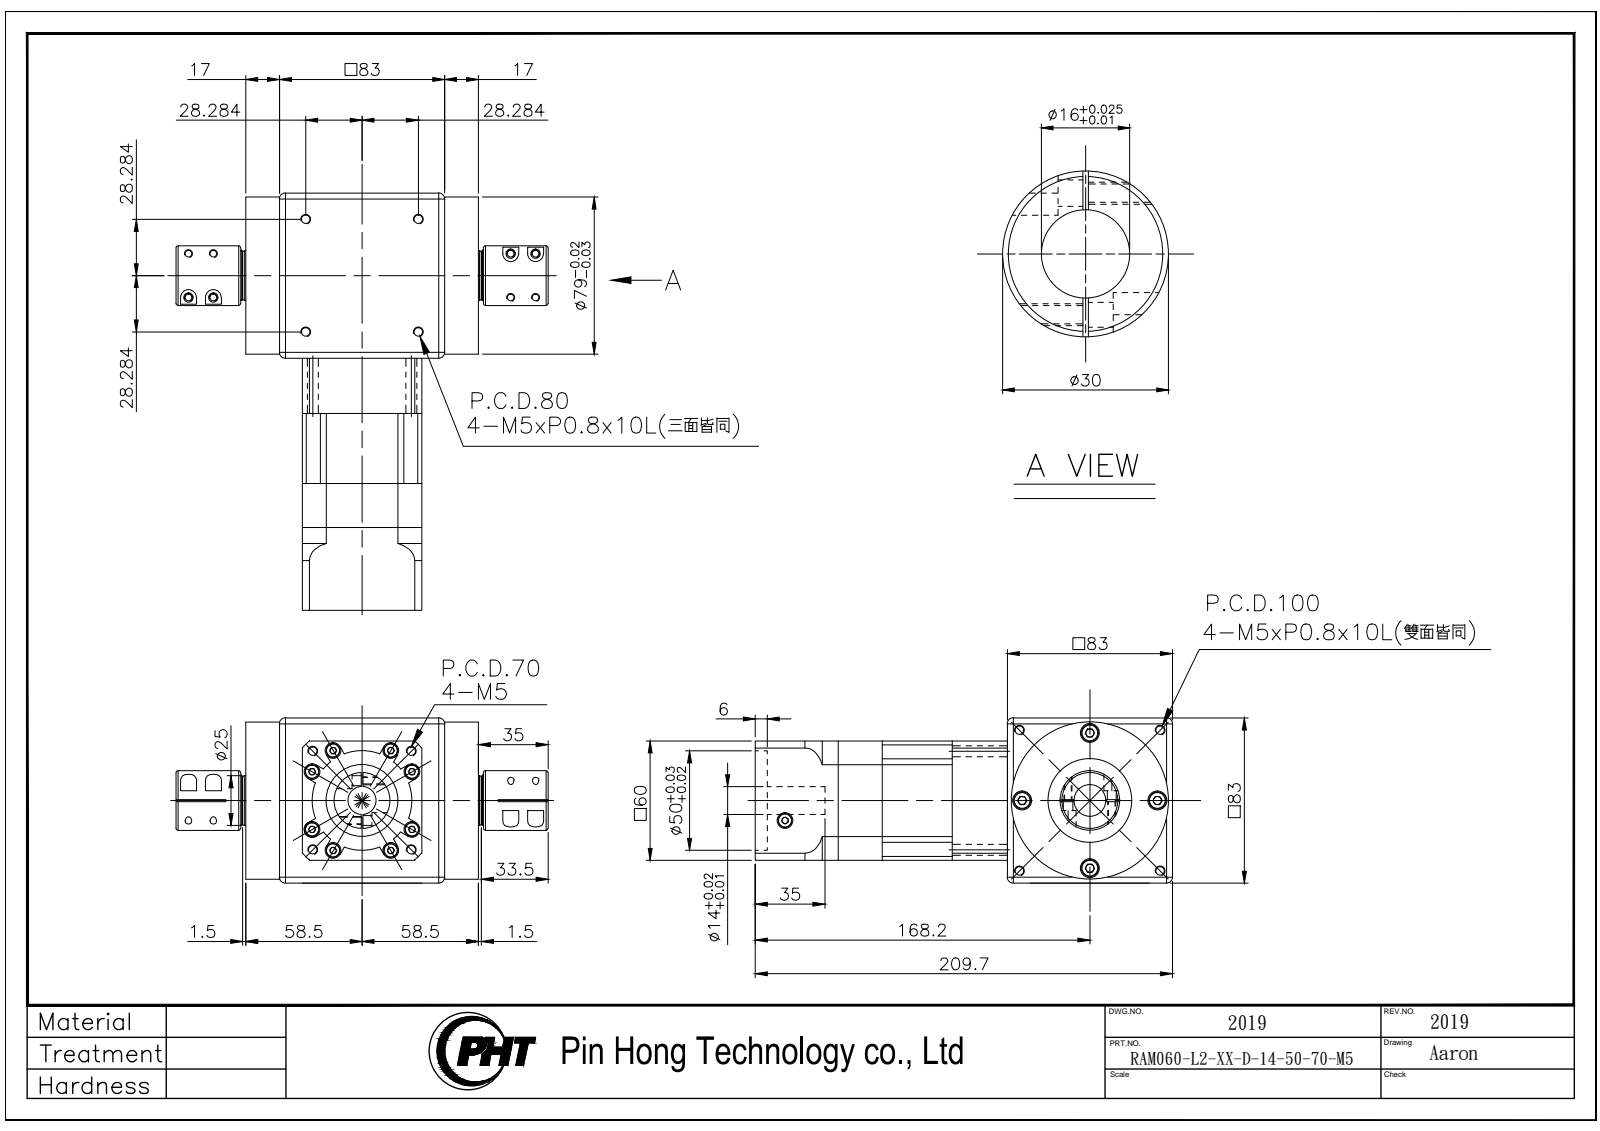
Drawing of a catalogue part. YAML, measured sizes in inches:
part_name: "RAM060-L2-XX-D-14-50-70-M5_2019"
step_written_by: "SolidWorks 2016 (AUTOMOTIVE_DESIGN)"
units: inches
bodies: {solids: 5, faces: 1110, planar: 545, cylindrical: 369, other: 196}
overall_size: [8.256, 7.362, 3.268]
volume: 68.9
surface_area: 239.7
round_holes:
  - {diameter: 0.165, count: 16}
  - {diameter: 0.315, count: 10}
  - {diameter: 0.161, count: 8}
  - {diameter: 0.177, count: 8}
  - {diameter: 0.189, count: 8}
  - {diameter: 0.217, count: 8}
  - {diameter: 0.374, count: 4}
  - {diameter: 0.551, count: 1}
  - {diameter: 0.63, count: 1}
  - {diameter: 0.654, count: 1}
  - {diameter: 1.417, count: 1}
round_bosses_or_shafts:
  - {diameter: 0.276, count: 16}
  - {diameter: 0.335, count: 8}
  - {diameter: 0.299, count: 8}
  - {diameter: 0.157, count: 8}
  - {diameter: 3.11, count: 1}
  - {diameter: 2.165, count: 1}
  - {diameter: 1.654, count: 1}
  - {diameter: 1.181, count: 1}
partial_cylinders:
  - {radius: 0.157, count: 8}
  - {radius: 0.197, count: 4}
  - {radius: 0.984, count: 1}
  - {radius: 1.378, count: 1}
  - {radius: 1.575, count: 1}
  - {radius: 2.25, count: 1}
face_to_face_distances: [2.815, 0.453, 3.268, 2.362, 1.122, 1.091, 2.258, 3.348, 0.872, 1.386]
hole_center_spacings: [1.142, 0.404, 0.557, 1.545, 1.615, 1.689, 2.004, 2.093]
